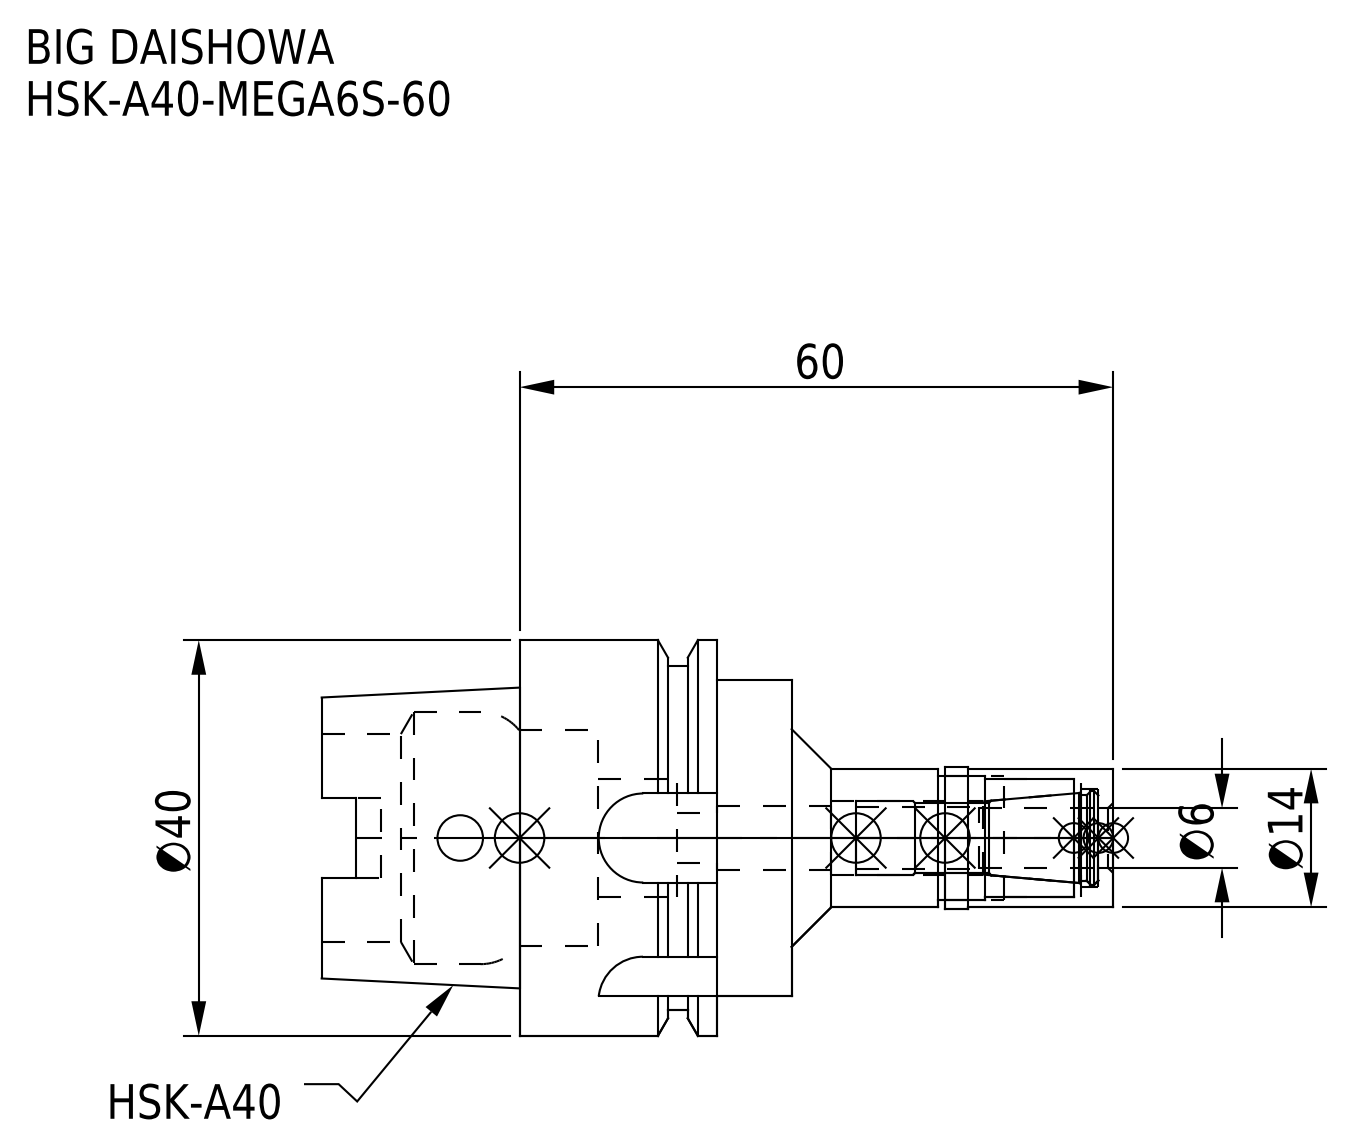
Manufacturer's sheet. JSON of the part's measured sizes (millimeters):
{"part_name": "HSK-A40-MEGA6S-60-060.stp; DXF_TEMP_ASSY_ASM_4_ASM.stp; MGN6S_1.stp; HSK-A40-MEGA6S-60 (+3 more)", "step_written_by": "SolidWorks 2019 (CONFIG_CONTROL_DESIGN)", "units": "millimeters", "bodies": {"solids": 2, "faces": 123, "planar": 47, "cylindrical": 56, "other": 20}, "overall_size": [80, 40, 40], "volume_mm3": 34004, "surface_area_mm2": 13806, "round_holes": [[4.6, 1], [5, 1], [6.1, 1], [6.4, 1], [7.4, 1], [10, 1], [12, 1], [12.5, 1], [21, 1], [21.8, 1], [25.5, 1]], "round_bosses_or_shafts": [[40, 1], [34.8, 1], [32, 1], [14.3, 1], [14, 1]], "partial_cylinders_radius": [[1.88, 4], [4.5, 4]], "face_to_face_distances": [20, 27.5, 7.5, 40, 19.55, 12.05, 7.95, 47.5, 27.95, 34]}
